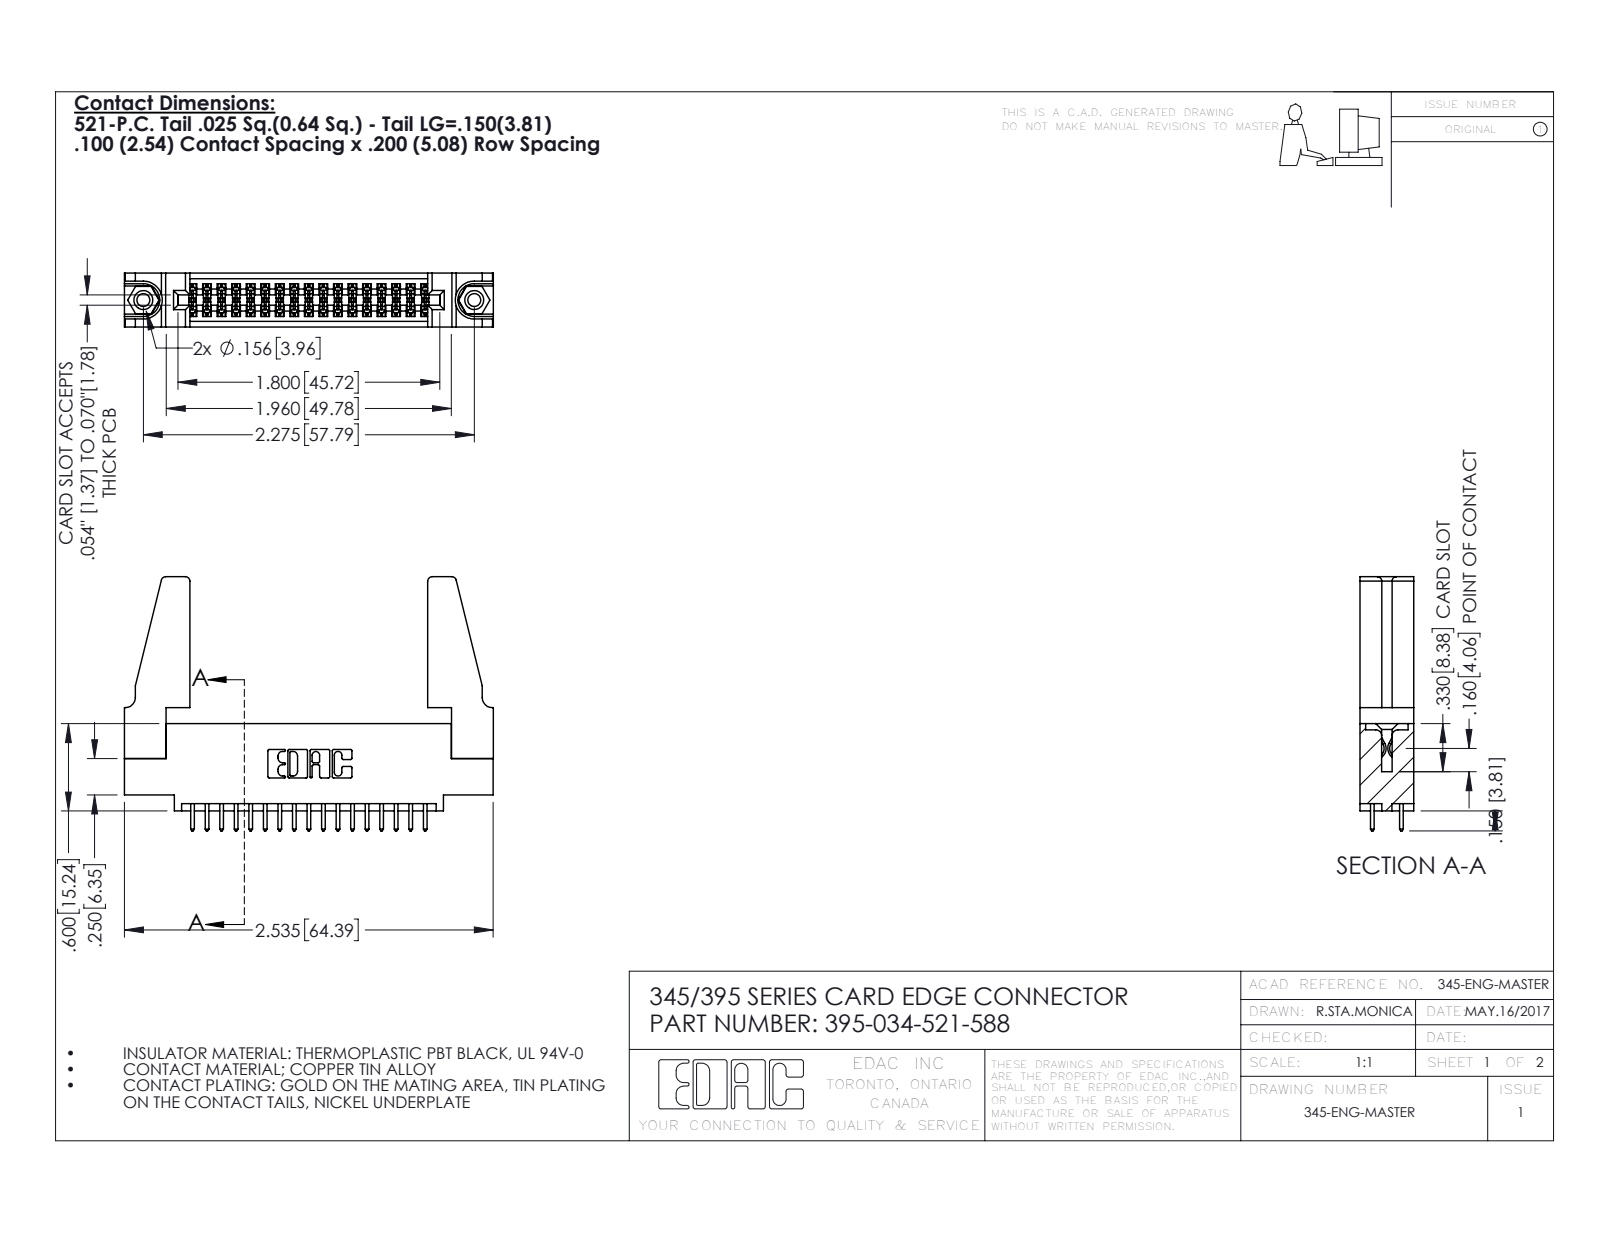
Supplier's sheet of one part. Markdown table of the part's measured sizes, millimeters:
| quantity | value |
| --- | --- |
| part name | 345-220-078_345-220-088; 395-034-521-588; 345 Part_0.110 Offset - 0.156 Dia-TH; 345-250-001_345-250-001-102 (+1 more) |
| STEP written by | SolidWorks 2016 (CONFIG_CONTROL_DESIGN) |
| units | millimeters |
| bodies | 39 solids, 1954 faces (1278 planar, 660 cylindrical, 16 other) |
| overall size | 64.4 × 44.4 × 9.4 |
| volume | 9 190 mm³ |
| surface area | 11 420 mm² |
| round holes (diameter × count) | 2.3 × 2, 3.2 × 2, 4 × 2, 1.6 × 1 |
| round bosses / shafts (diameter × count) | 3.9 × 2 |
| partial cylindrical surfaces (radius × count) | 0.2 × 51, 0.3 × 34, 0.3 × 22, 0.8 × 8, 0.2 × 6, 0.8 × 6, 0.7 × 3, 0.4 × 2 |
| main face-to-face distances | 1.8, 9.4, 7.6, 5.1, 2.5, 6.9, 0.6, 5.7, 4.4, 3.8 |
| hole center spacings | 6.9, 51.8, 57.8 |
